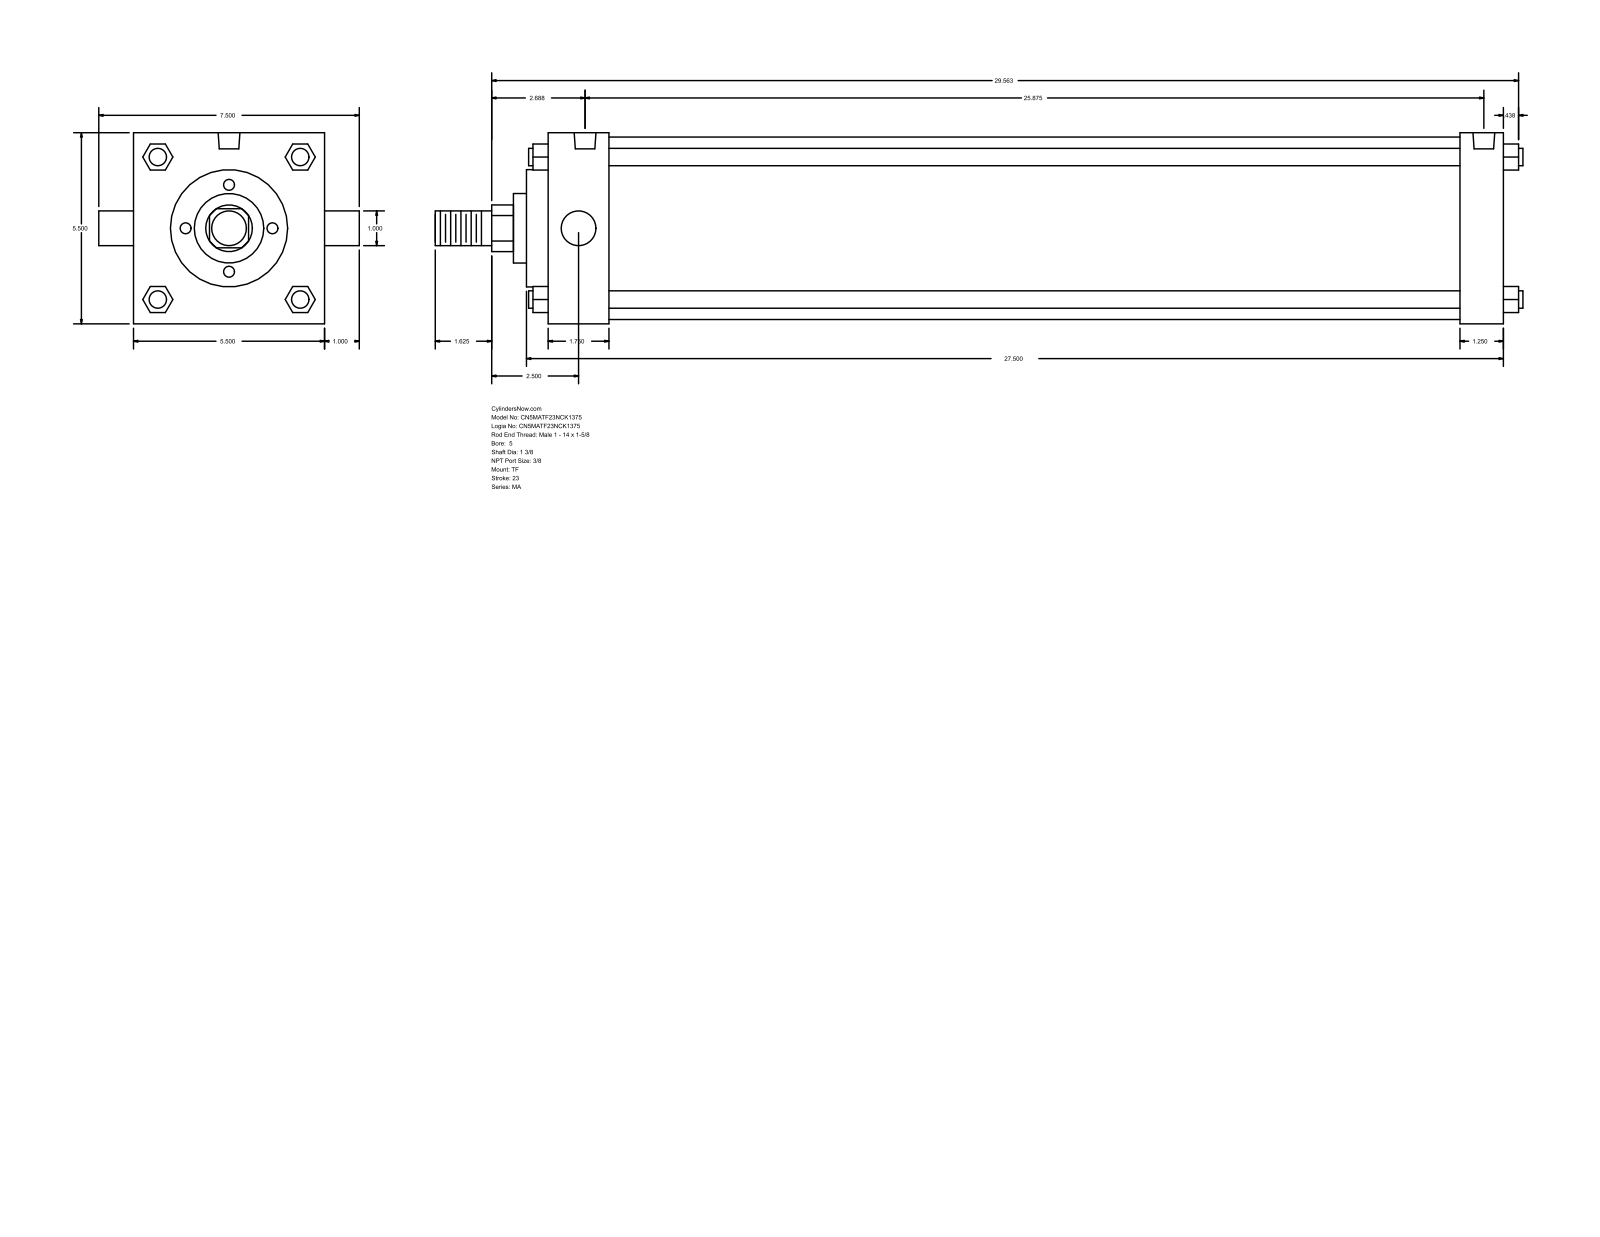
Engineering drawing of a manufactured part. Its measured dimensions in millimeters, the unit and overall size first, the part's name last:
Units: millimetres
Overall size (bounding box): 795.34 × 190.5 × 139.7
Round holes (diameter × count): ⌀11.11 ×3, ⌀15.93 ×2
Round bosses / shafts (diameter × count): ⌀12.7 ×4, ⌀25.4 ×2, ⌀133.35 ×1, ⌀85.72 ×1, ⌀50.8 ×1, ⌀34.92 ×1
Partial cylindrical surfaces — rounded edges, fillets, slot ends (radius × count): R17.06 ×1
Main face-to-face distances: 139.7, 698.5, 666.75, 31.75, 44.45, 622.3, 654.05, 15.87, 60.32, 682.62
Hole centre spacings: 4.76, 4.77, 647.7, 652.46, 652.47, 657.23
Bodies: 0 solids, 122 faces (93 planar, 29 cylindrical, 0 other)
Part name (STEP PRODUCT): MA_TF__0500_1.375
STEP written by: GSSL Pune (CONFIG_CONTROL_DESIGN)
